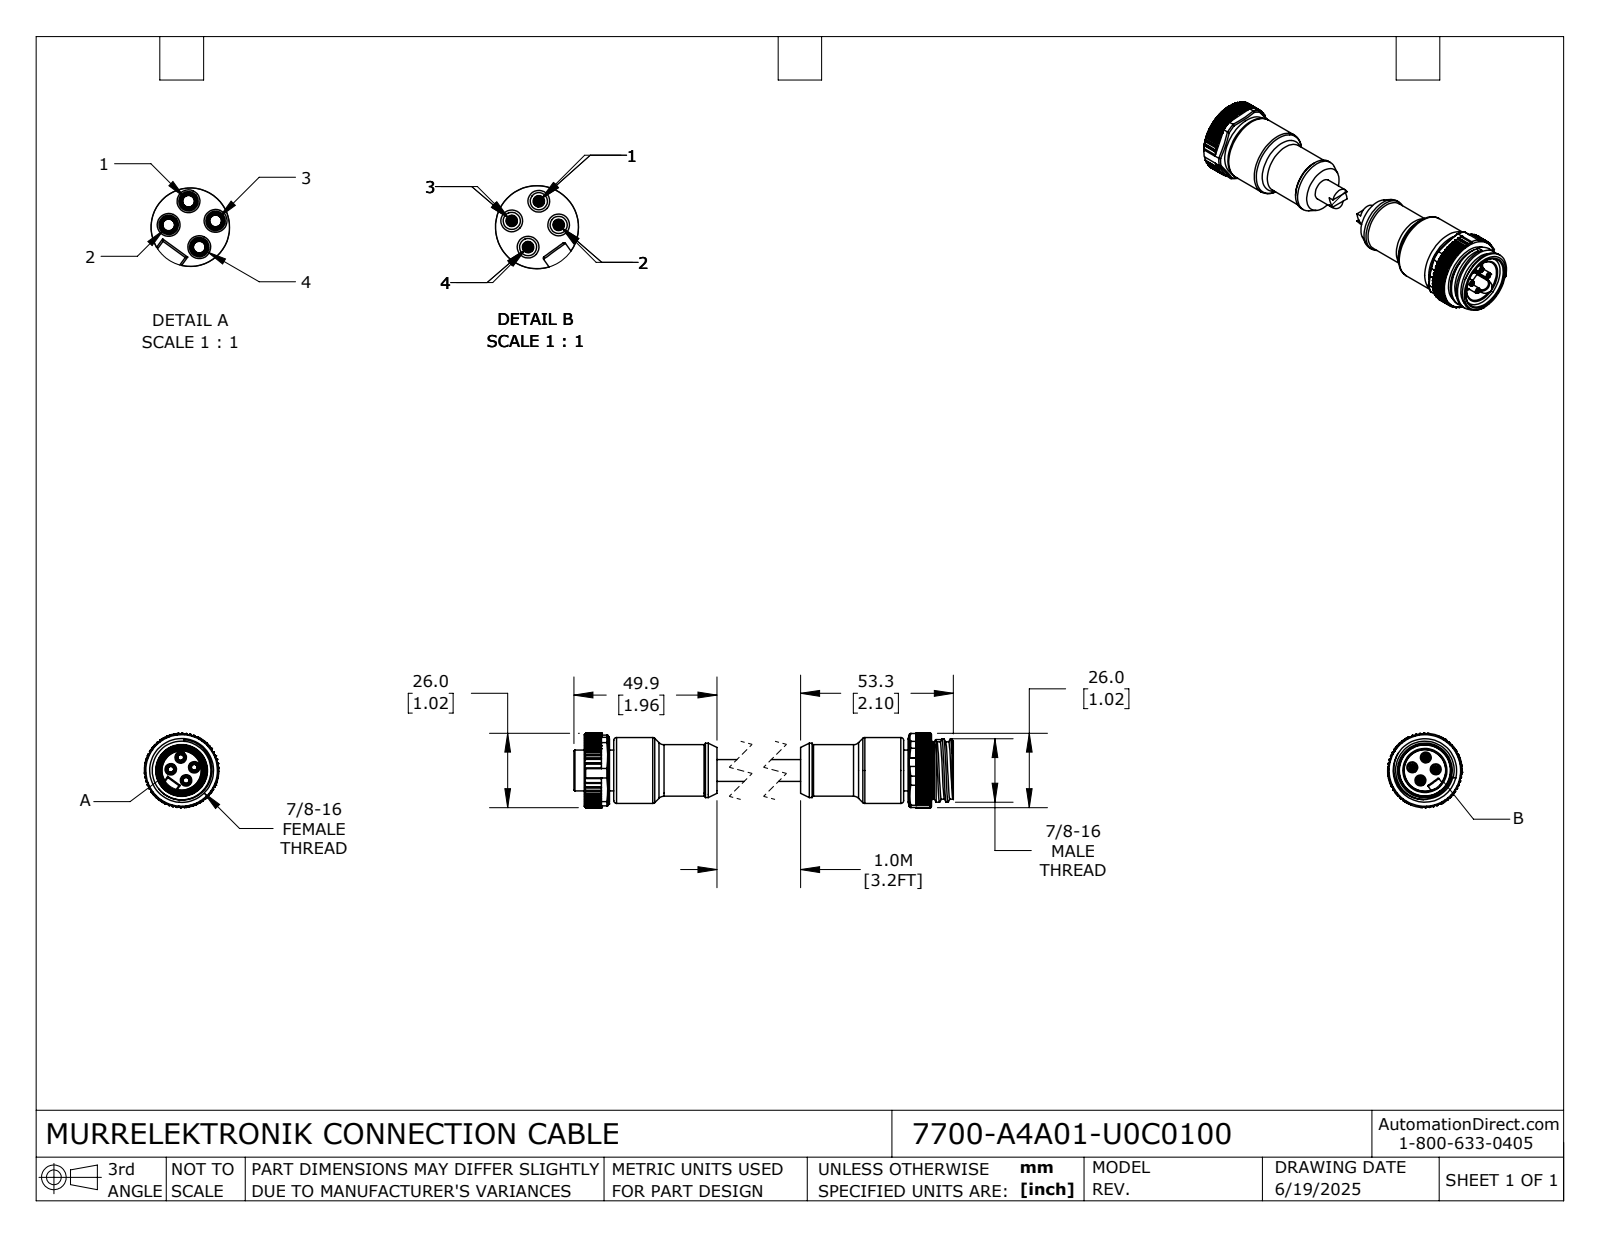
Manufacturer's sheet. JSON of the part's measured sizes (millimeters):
{"part_name": "7700-A4A01-U0C0100_MALE; 7700-A4A01-U0C0100; 7700-A4A01-U0C0100_FEMALE", "step_written_by": "SolidWorks 2024 (CONFIG_CONTROL_DESIGN)", "units": "millimeters", "bodies": {"solids": 2, "faces": 1226, "planar": 520, "cylindrical": 543, "other": 163}, "overall_size": [133.2, 26, 26], "volume_mm3": 33740, "surface_area_mm2": 14250, "round_holes": [[2.1, 4], [3, 4], [3.4, 4], [15.5, 1], [15.6, 1], [18.5, 1], [20.5, 1], [22.2, 1]], "round_bosses_or_shafts": [[2, 4], [23, 1], [22.2, 1], [20, 1], [20, 1], [19, 1], [18.1, 1], [18, 1]], "partial_cylinders_radius": [[0.2, 252], [0.3, 18], [0.1, 8], [0.7, 4], [0.7, 4], [2.4, 1], [13, 1]], "face_to_face_distances": [1.5, 103.5, 37.5, 67.5, 36, 66, 105, 8.8, 112.3, 7.3], "hole_center_spacings": [3.8, 8.2, 4.5, 4.5, 5.4, 5.4, 5.8, 6.6]}
